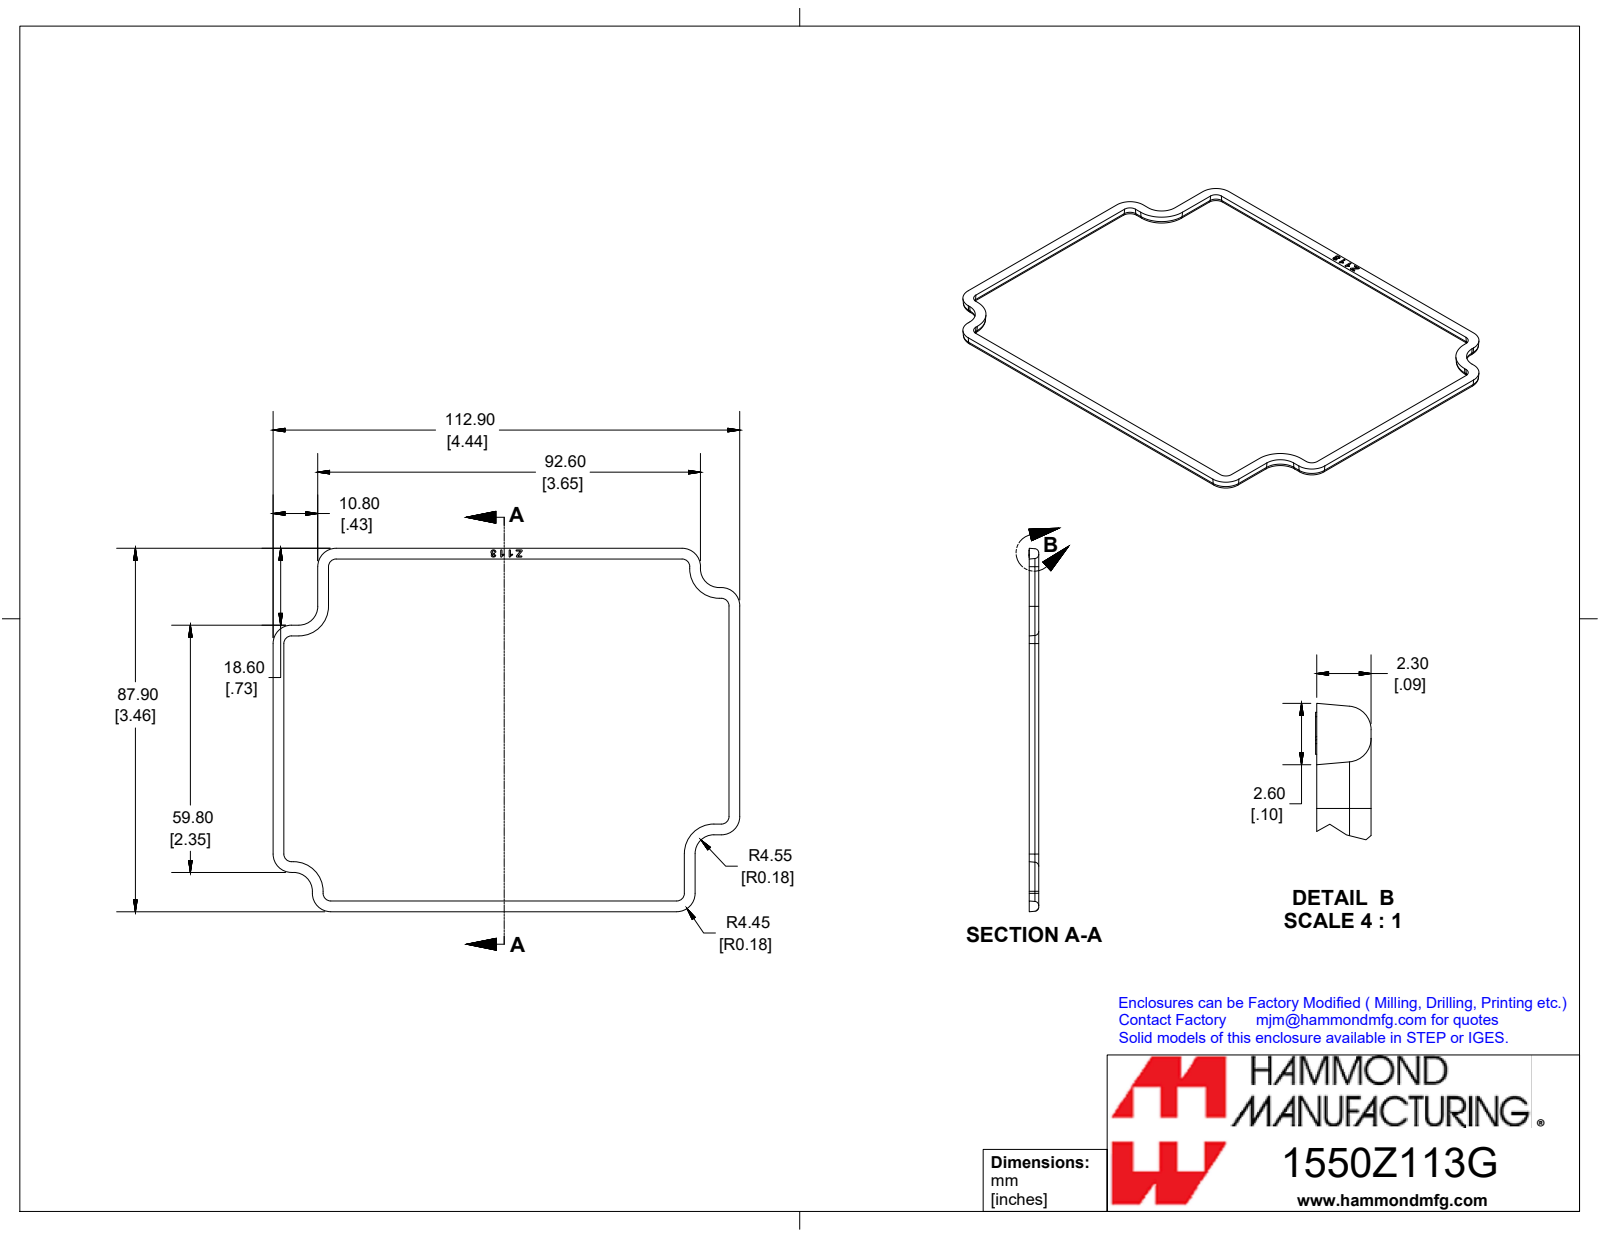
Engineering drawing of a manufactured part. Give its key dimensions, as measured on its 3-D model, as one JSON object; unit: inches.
{"part_name": "1550Z113GASKET", "step_written_by": "SolidWorks 2019 (CONFIG_CONTROL_DESIGN)", "units": "inches", "bodies": {"solids": 1, "faces": 154, "planar": 41, "cylindrical": 24, "other": 89}, "overall_size": [4.445, 3.461, 0.093], "volume_in3": 0.117, "surface_area_in2": 5.006, "partial_cylinders_radius": [[0.039, 24]], "face_to_face_distances": [3.344, 4.325, 0.091, 0.423, 3.902, 3.478, 0.729, 2.615, 0.372, 1.886]}
